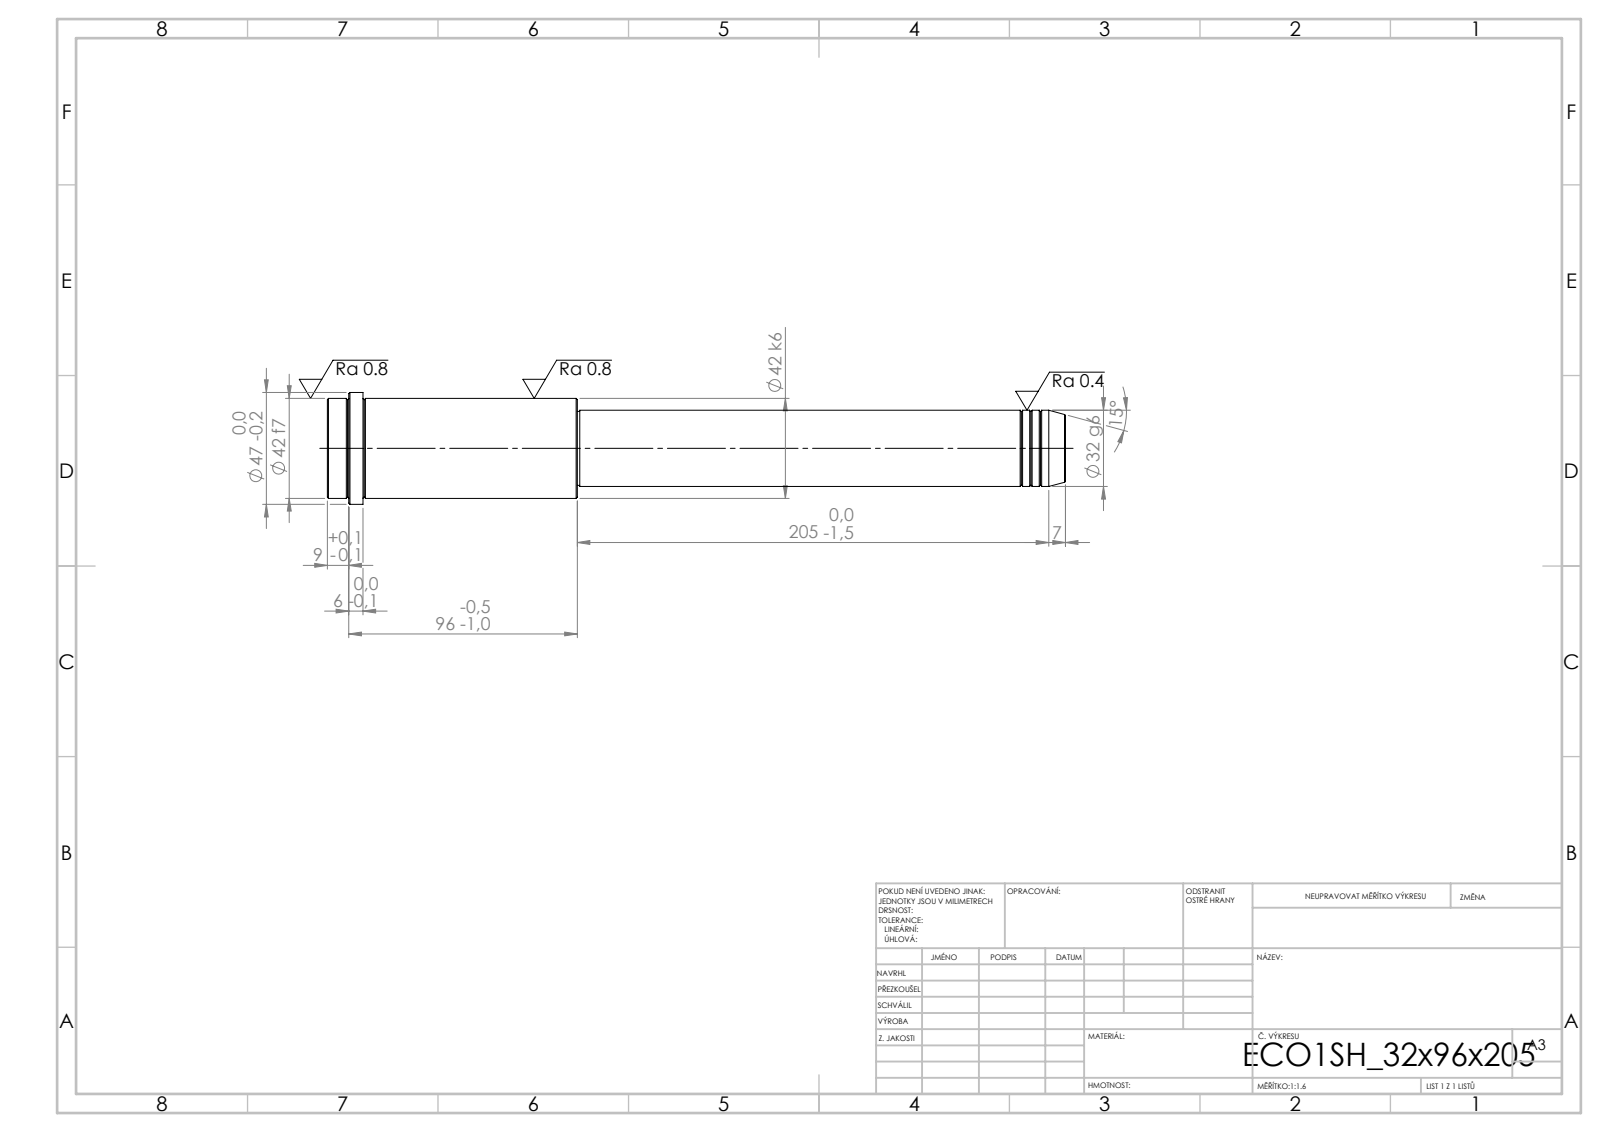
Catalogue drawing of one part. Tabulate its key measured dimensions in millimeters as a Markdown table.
| quantity | value |
| --- | --- |
| STEP written by | SolidWorks 2019 (CONFIG_CONTROL_DESIGN) |
| units | millimeters |
| bodies | 1 solid, 52 faces (6 planar, 16 cylindrical, 30 other) |
| overall size | 310 × 47 × 47 |
| volume | 311 483 mm³ |
| surface area | 38 103 mm² |
| round bosses / shafts (diameter × count) | 47 × 1, 42 × 1, 32 × 1, 31 × 1 |
| main face-to-face distances | 310, 205, 105, 295, 90, 15, 301, 96, 6, 9 |
